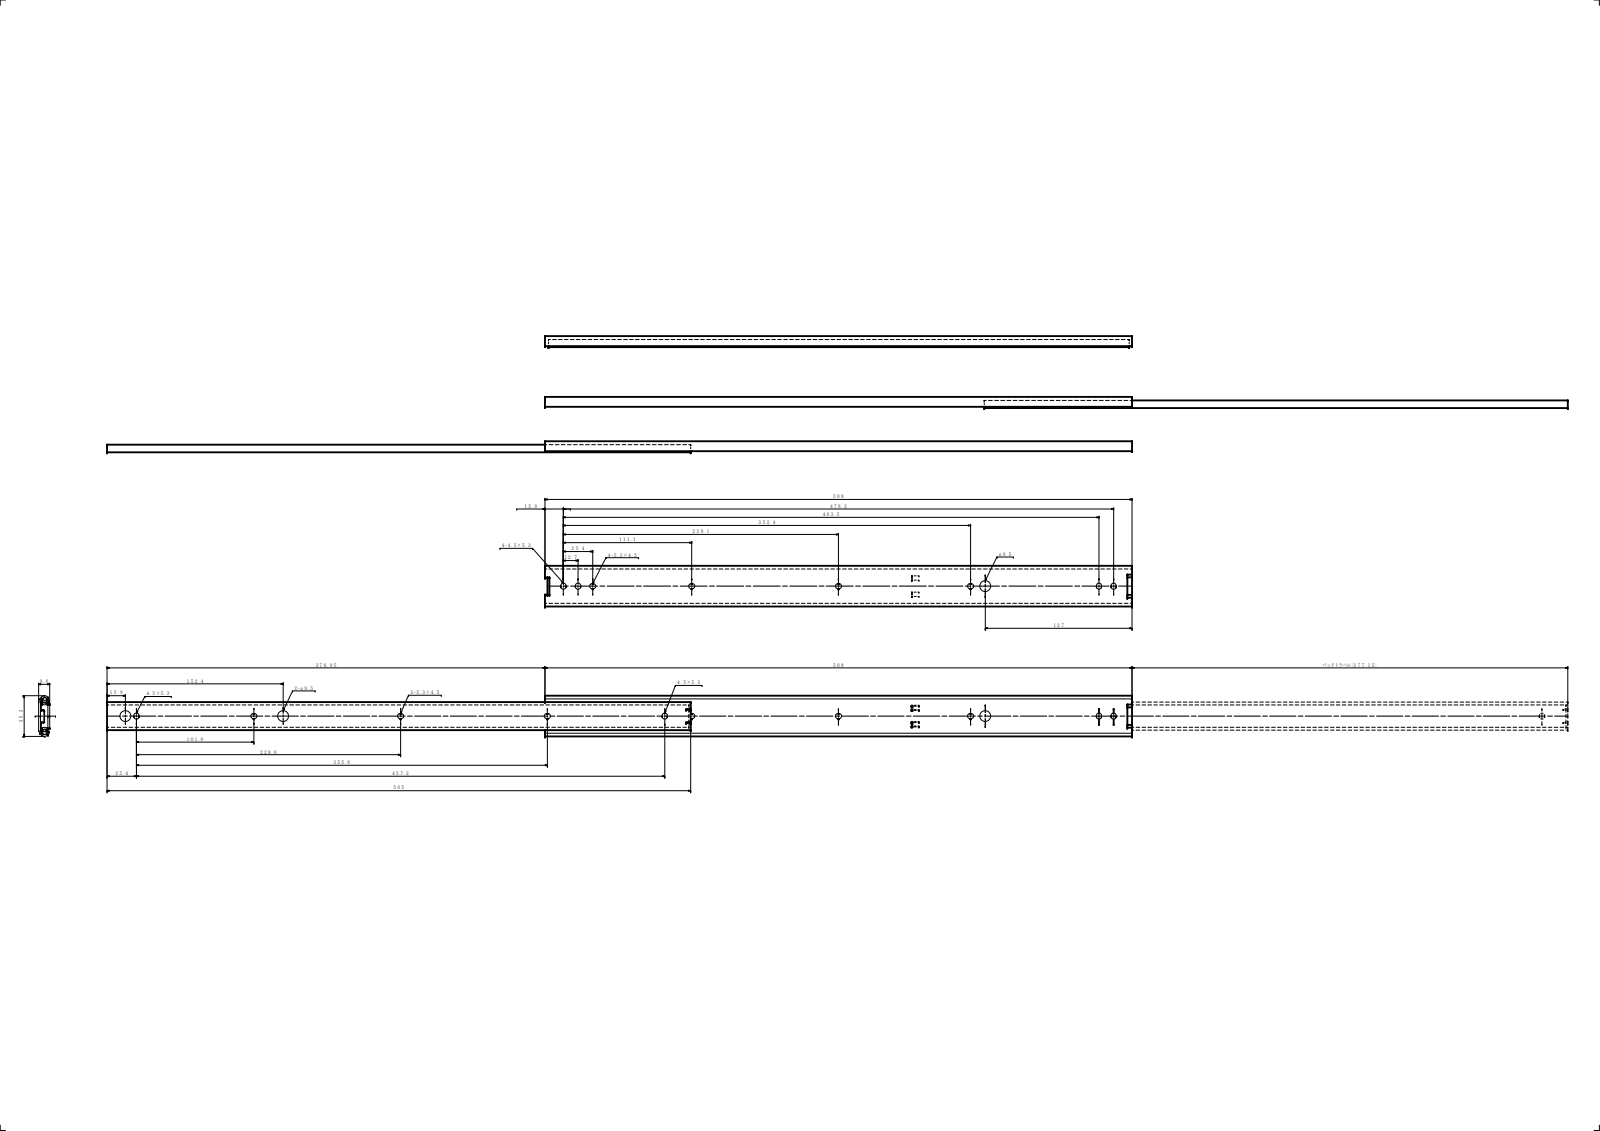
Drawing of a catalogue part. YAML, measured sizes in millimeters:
part_name: "IM 3520-20; 3520-20; OM 3520-20"
step_written_by: "SolidWorks 2019 (CONFIG_CONTROL_DESIGN)"
units: millimeters
bodies: {solids: 2, faces: 147, planar: 72, cylindrical: 75, other: 0}
overall_size: [886.95, 35.3, 9.6]
volume: 63511
surface_area: 83391
round_holes:
  - {diameter: 9.5, count: 3}
partial_cylinders:
  - {radius: 2.25, count: 26}
  - {radius: 0.4, count: 6}
  - {radius: 1, count: 4}
  - {radius: 2.5, count: 4}
  - {radius: 3, count: 4}
  - {radius: 0.2, count: 2}
  - {radius: 1.8, count: 2}
  - {radius: 2, count: 2}
face_to_face_distances: [1.6, 8, 9.6, 6.4, 1.3, 6.7, 2.9, 5.1, 4.67, 3.07]
hole_center_spacings: [136.5, 607.55, 744.05]
